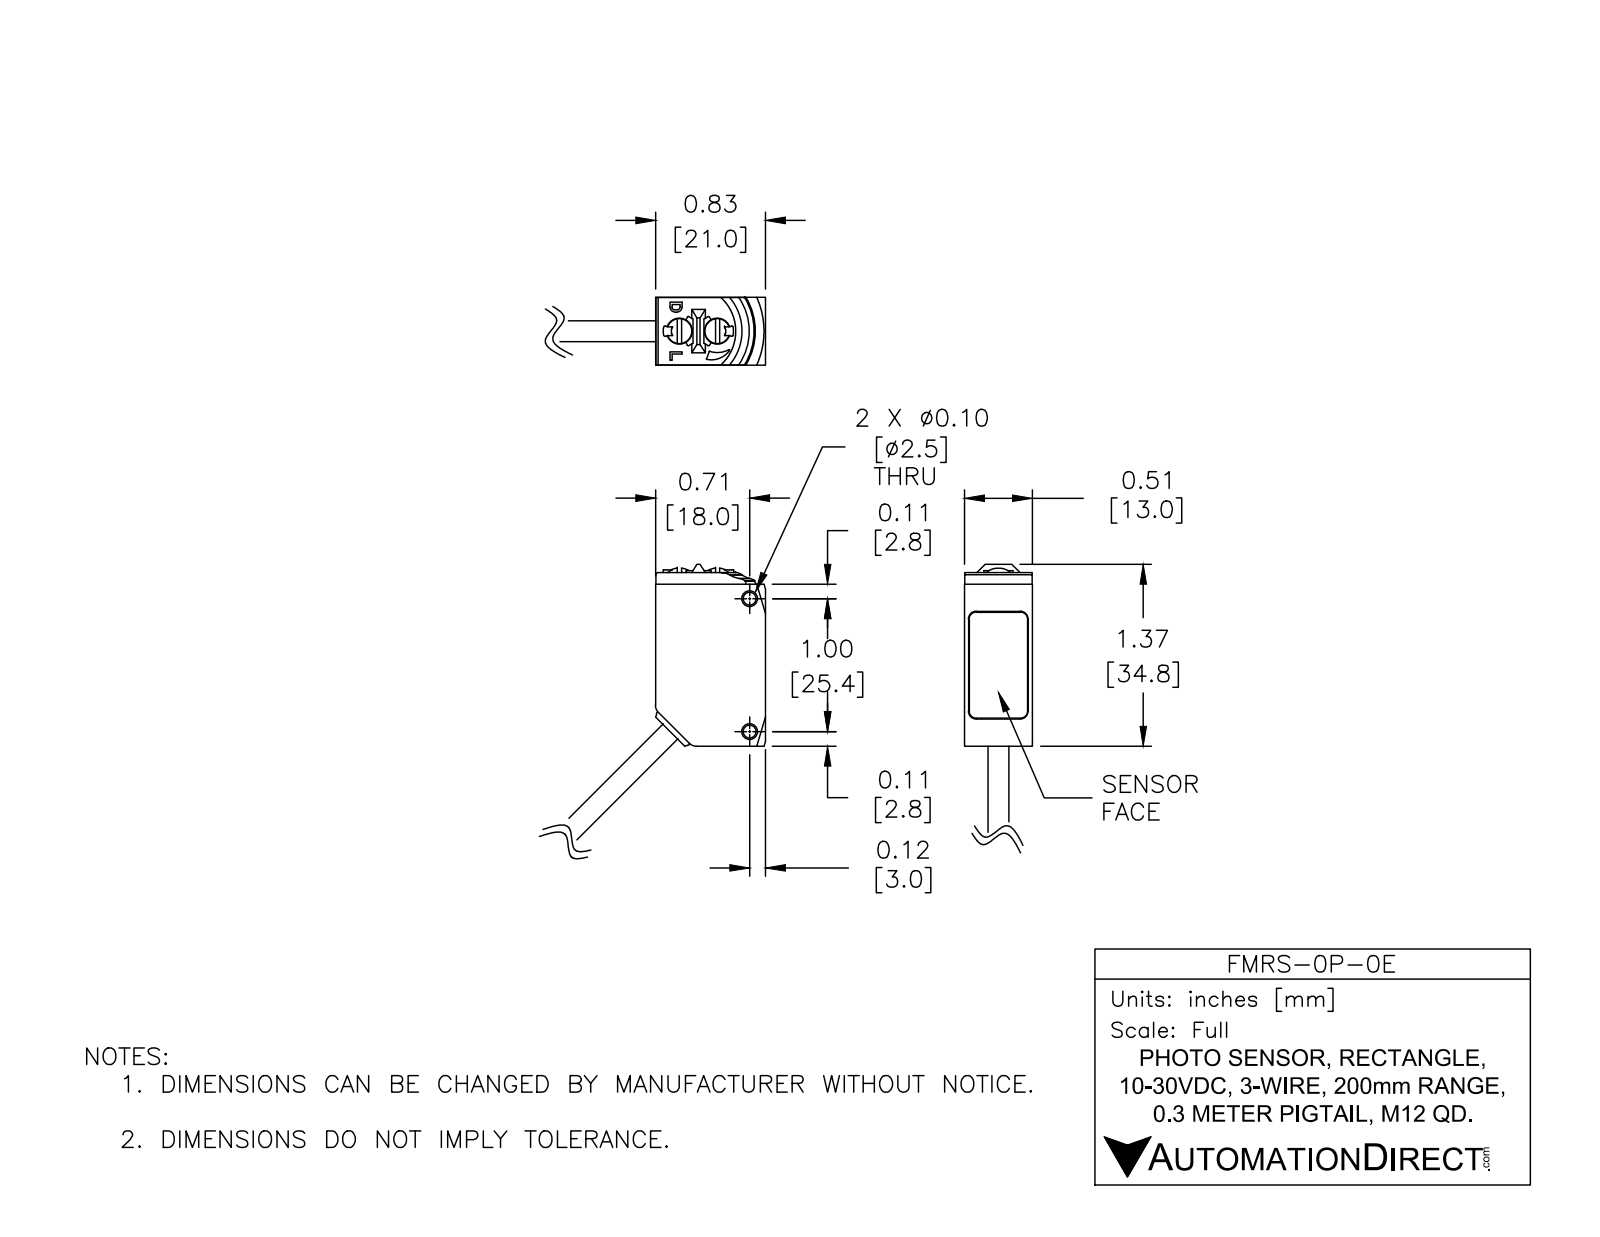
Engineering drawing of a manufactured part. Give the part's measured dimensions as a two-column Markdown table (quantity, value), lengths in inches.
| quantity | value |
| --- | --- |
| part name | FMRS-0P-0E |
| STEP written by | SolidWorks 2017 (AUTOMOTIVE_DESIGN) |
| units | inches |
| bodies | 1 solid, 186 faces (89 planar, 72 cylindrical, 25 other) |
| overall size | 2.084 × 1.541 × 0.512 |
| volume | 0.542 in³ |
| surface area | 5.476 in² |
| round holes (diameter × count) | 0.097 × 2, 0.197 × 2 |
| round bosses / shafts (diameter × count) | 0.189 × 2, 0.157 × 1 |
| partial cylindrical surfaces (radius × count) | 0.018 × 7, 0.02 × 7, 0.008 × 4, 0.01 × 4, 0.051 × 4, 0.059 × 4, 0.004 × 3, 0.018 × 2 |
| main face-to-face distances | 0.512, 0.827, 1.307, 0.035, 0.51, 0.031, 0.48, 0.037, 0.474, 0.472 |
| hole center spacings | 0.287, 1 |
